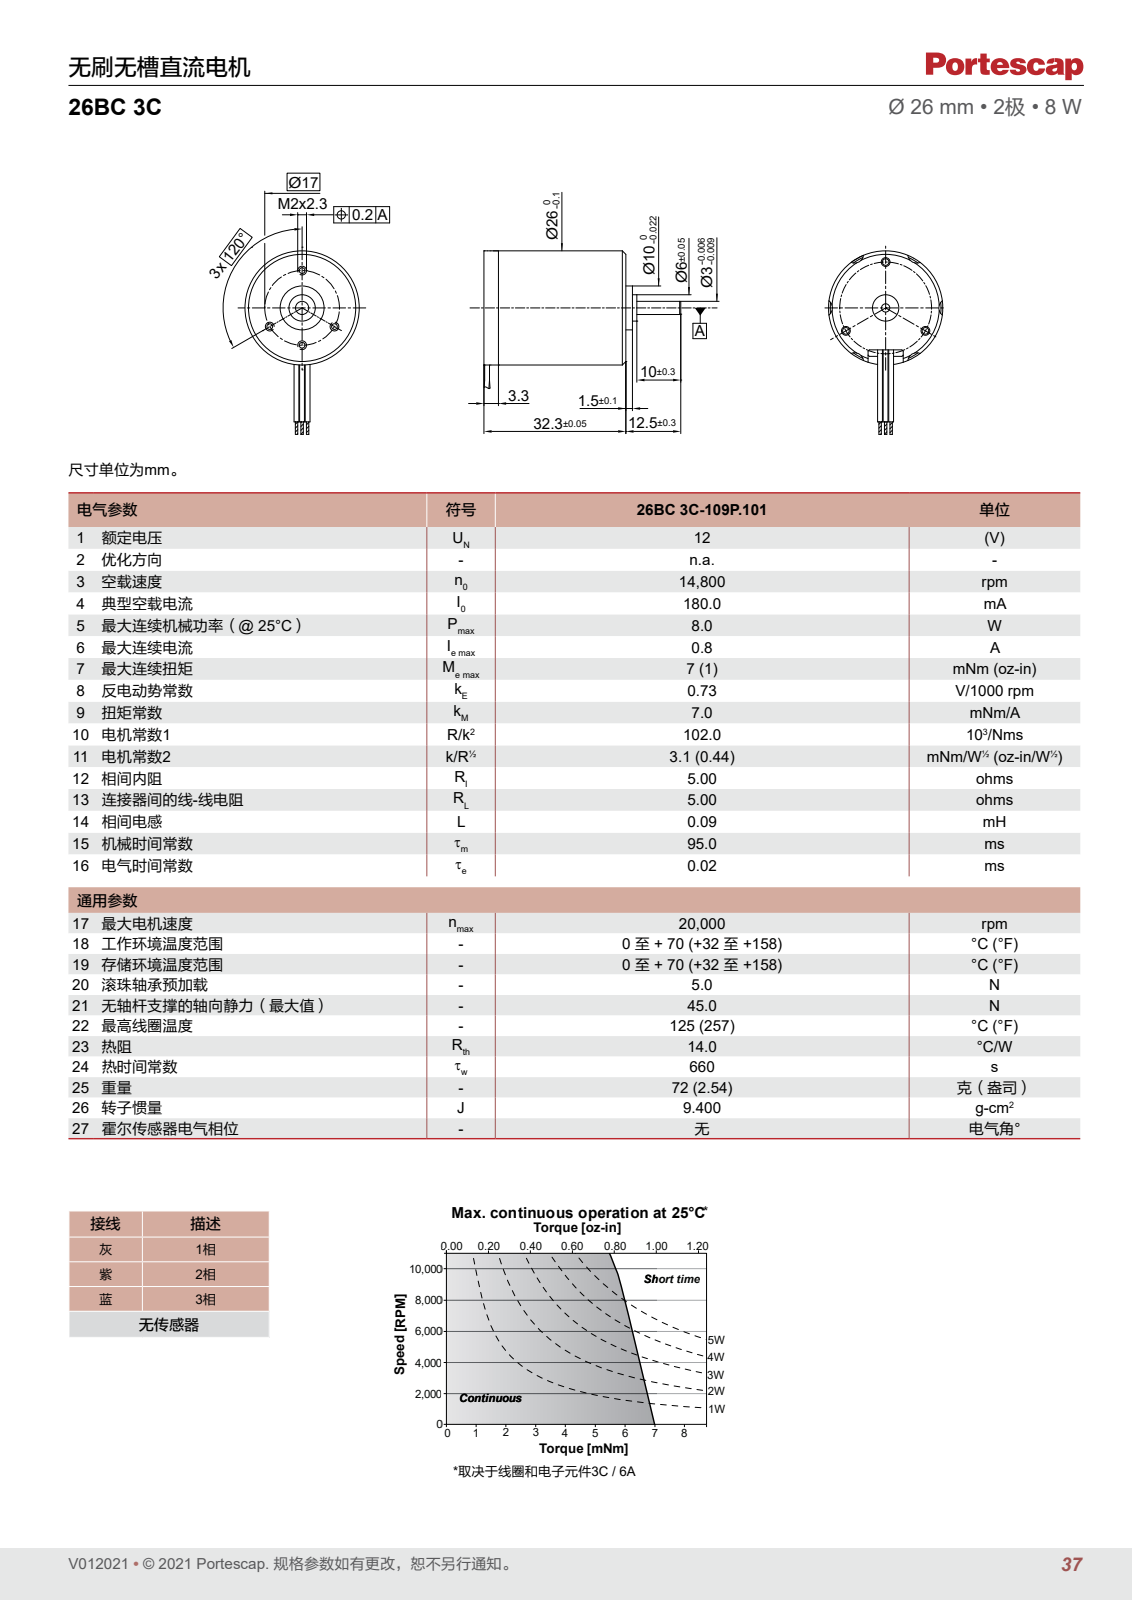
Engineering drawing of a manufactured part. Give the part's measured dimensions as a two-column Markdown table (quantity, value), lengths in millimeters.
| quantity | value |
| --- | --- |
| part name | 26BC_3C_ASM |
| STEP written by | PRO/ENGINEER BY PARAMETRIC TECHNOLOGY CORPORATION, 2014310 (CONFIG_CONTROL_DESIGN) |
| units | millimeters |
| bodies | 4 solids, 208 faces (52 planar, 99 cylindrical, 57 other) |
| overall size | 76.09 × 44.8 × 26 |
| volume | 17 217 mm³ |
| surface area | 4 503 mm² |
| round holes (diameter × count) | 2 × 13, 1.6 × 4, 1.5 × 3, 6 × 1, 8 × 1 |
| round bosses / shafts (diameter × count) | 1 × 6, 0.4 × 6, 0.8 × 3, 26 × 1, 10 × 1, 3 × 1 |
| partial cylindrical surfaces (radius × count) | 2 × 6, 0.5 × 1 |
| main face-to-face distances | 32.3, 1.5, 33.8, 32.7, 31.2, 1.1, 2.5, 0.7, 31.5, 33.1 |
| hole center spacings | 7.7, 8.5, 16.44, 3.97, 11.25, 11.68, 13.33, 1.95 |
